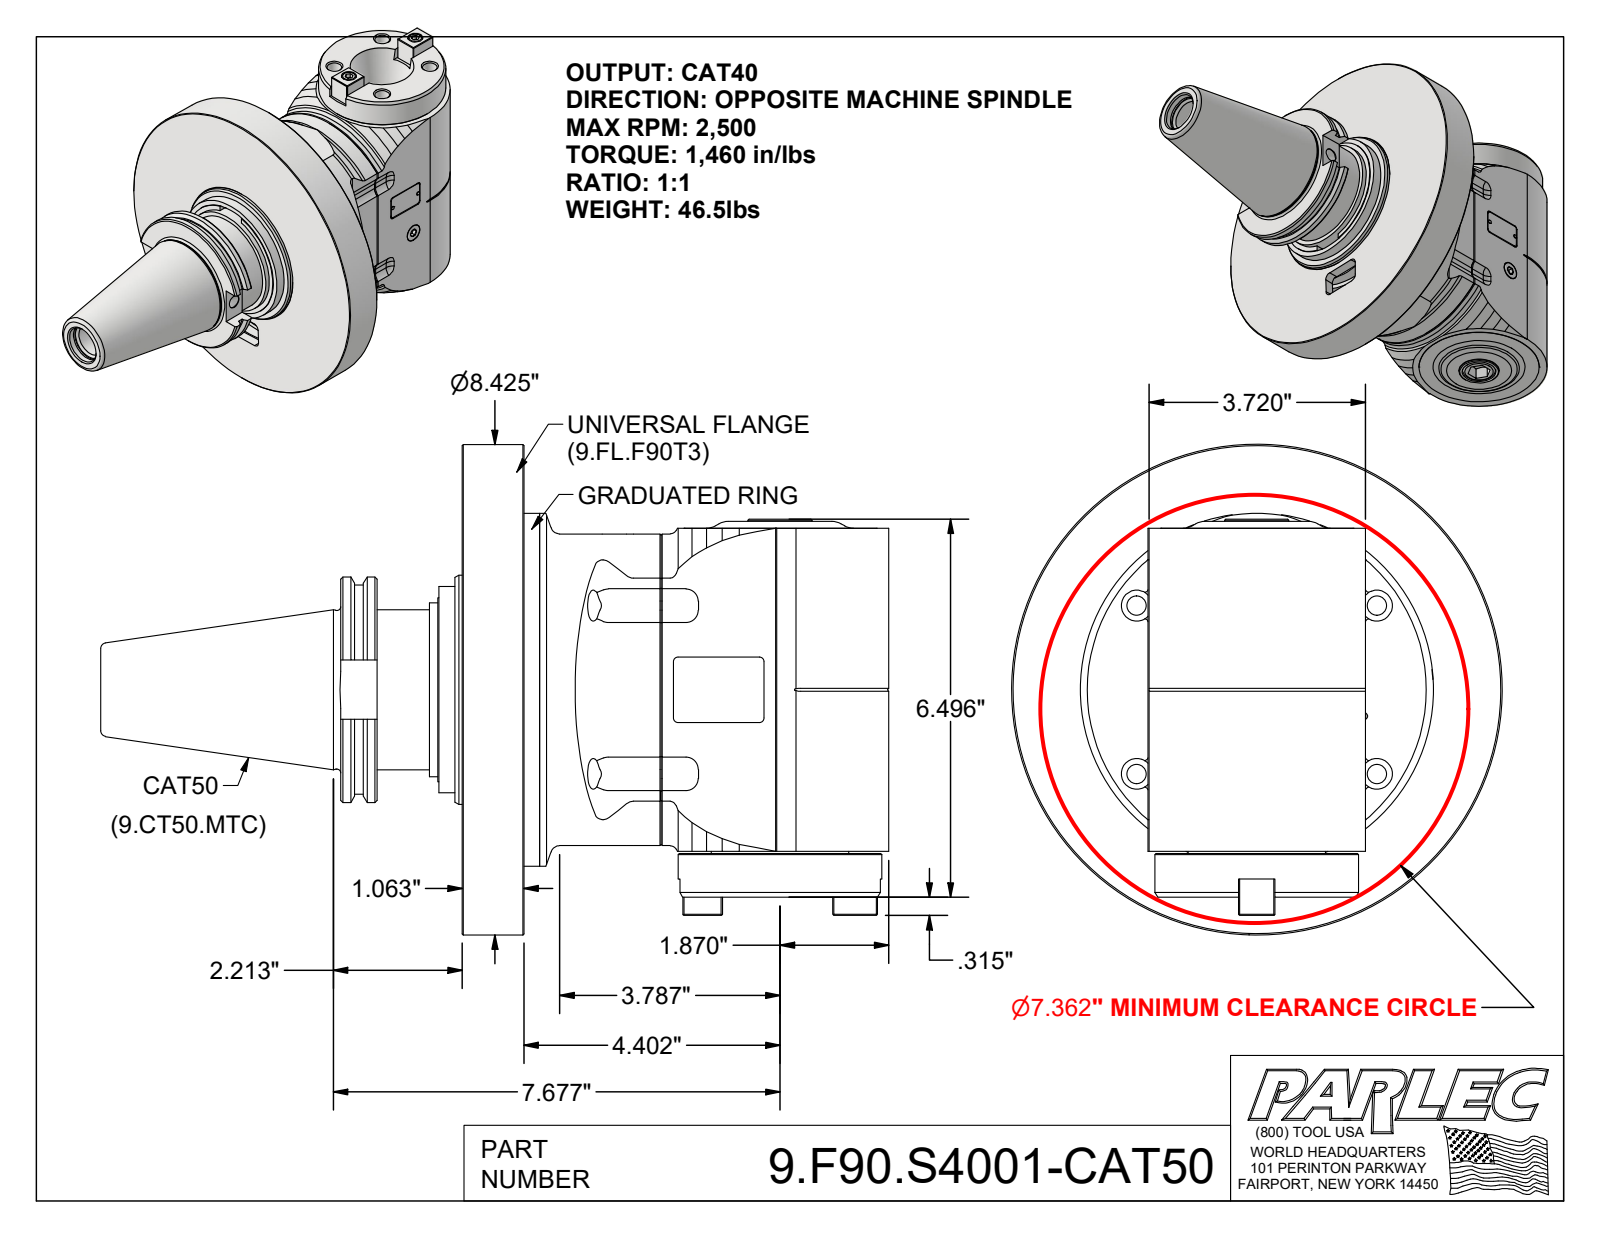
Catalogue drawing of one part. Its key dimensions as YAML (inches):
part_name: "9.F90.S4001-CAT50; 9_SK_45_2 (Cat50, MTC); 9_FL_F90T3 (MTC, Universal Flange, Type 3); 9_F90_S4001"
step_written_by: "Autodesk Inventor 2022 (AUTOMOTIVE_DESIGN)"
units: inches
bodies: {solids: 4, faces: 468, planar: 196, cylindrical: 122, other: 150}
overall_size: [13.547, 8.425, 8.425]
volume: 214.1
surface_area: 496.6
round_holes:
  - {diameter: 0.335, count: 4}
  - {diameter: 0.404, count: 4}
  - {diameter: 0.531, count: 4}
  - {diameter: 0.413, count: 2}
  - {diameter: 0.375, count: 1}
  - {diameter: 0.492, count: 1}
  - {diameter: 0.65, count: 1}
  - {diameter: 0.787, count: 1}
  - {diameter: 0.865, count: 1}
  - {diameter: 0.925, count: 1}
  - {diameter: 0.996, count: 1}
  - {diameter: 1.031, count: 1}
round_bosses_or_shafts:
  - {diameter: 0.394, count: 2}
  - {diameter: 0.098, count: 2}
  - {diameter: 8.425, count: 1}
  - {diameter: 6.063, count: 1}
  - {diameter: 4.634, count: 1}
  - {diameter: 4.398, count: 1}
  - {diameter: 3.875, count: 1}
  - {diameter: 3.594, count: 1}
partial_cylinders:
  - {radius: 0.079, count: 12}
  - {radius: 0.276, count: 12}
  - {radius: 0.157, count: 8}
  - {radius: 1.87, count: 1}
  - {radius: 2.677, count: 1}
  - {radius: 2.913, count: 1}
face_to_face_distances: [1.063, 0.74, 0.323, 1.161, 1.484, 0.421, 3.74, 0.197, 1.287, 0.256]
hole_center_spacings: [0.996, 1.313, 1.857, 2.404, 2.52, 1.289, 2.626, 2.891]
